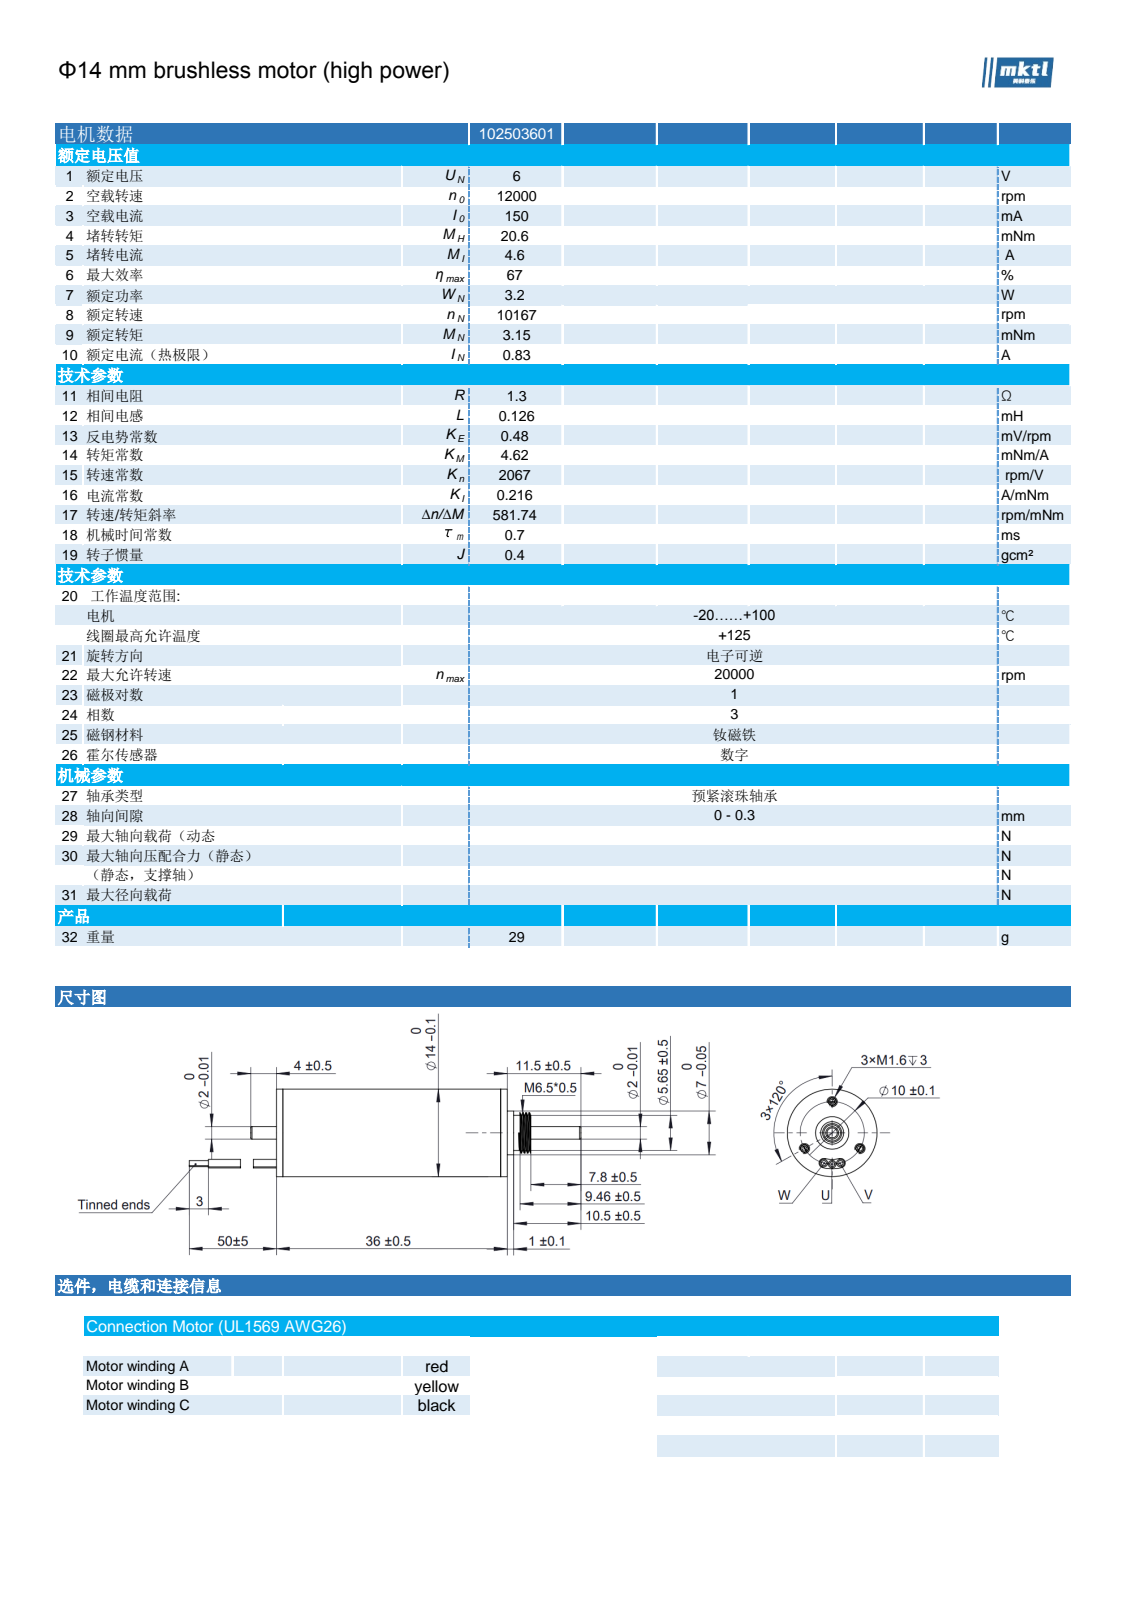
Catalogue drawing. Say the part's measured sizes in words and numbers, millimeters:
The part is named "approval 102503601". Its 3-D file was written by "SolidWorks 2025 (AUTOMOTIVE_DESIGN)". It is 167 solids with 1154 faces: 367 planar, 734 cylindrical and 53 other. Overall it measures 59.6 by 14 by 14 millimeters. Its volume is 5 222 cubic millimeters and its surface area 26 748 square millimeters. Round holes: 6 of diameter 0.8, 3 of diameter 1.1, 3 of diameter 1.2, 3 of diameter 1.25, 1 of diameter 3, 1 of diameter 4, 1 of diameter 5, 1 of diameter 5.2, 1 of diameter 6, 1 of diameter 7, 1 of diameter 7.1, 1 of diameter 9.8. Round bosses or shafts: 3 of diameter 1.2, 3 of diameter 0.58, 1 of diameter 14, 1 of diameter 13.2, 1 of diameter 13.12, 1 of diameter 13.1, 1 of diameter 6.6, 1 of diameter 6.5. Partial cylindrical surfaces (rounded edges, fillets, slot ends): 2 of radius 0.75, 1 of radius 4.25, 1 of radius 5.75. The main face-to-face distances are 0.4, 0.8, 0.6, 1, 1.2, 1.4, 1.6, 1.8, 2, 2.2. The hole center spacings are 5, 8.66, 1.3, 3.83, 6.08, 9.91, 2.58, 10.
